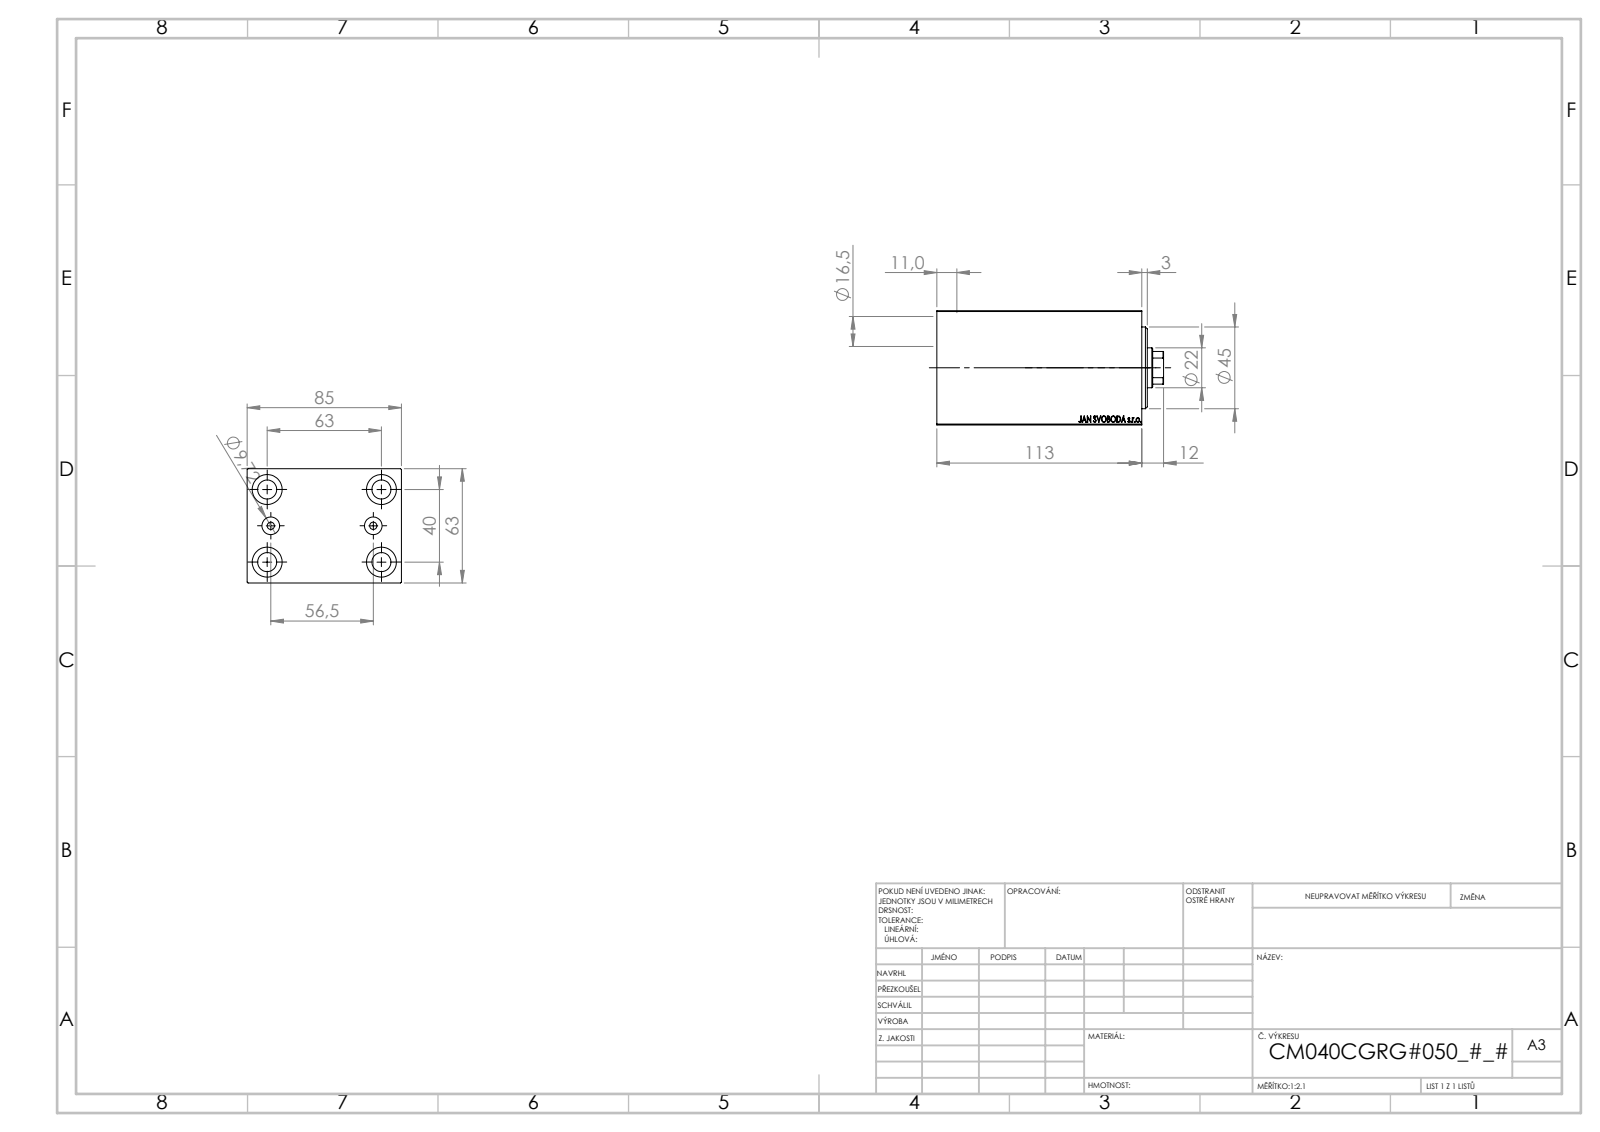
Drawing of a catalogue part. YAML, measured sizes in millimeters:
part_name: "V450CM_C_Body; V450CM_C_VCP; V450CM_VC_B"
step_written_by: "SolidWorks 2019 (CONFIG_CONTROL_DESIGN)"
units: millimeters
bodies: {solids: 3, faces: 858, planar: 408, cylindrical: 56, other: 394}
overall_size: [125, 85, 63]
volume: 511821
surface_area: 94535
round_holes:
  - {diameter: 10.5, count: 4}
  - {diameter: 16.5, count: 4}
  - {diameter: 4, count: 2}
  - {diameter: 9.72, count: 2}
  - {diameter: 12.5, count: 1}
  - {diameter: 22, count: 1}
  - {diameter: 25.5, count: 1}
  - {diameter: 40, count: 1}
  - {diameter: 42, count: 1}
  - {diameter: 45, count: 1}
partial_cylinders:
  - {radius: 10.5, count: 1}
face_to_face_distances: [63, 85, 12, 101, 113, 51, 1, 89, 11, 102]
hole_center_spacings: [37.31, 20.1, 20.5, 40, 61.82, 63, 64.2, 74.63]
